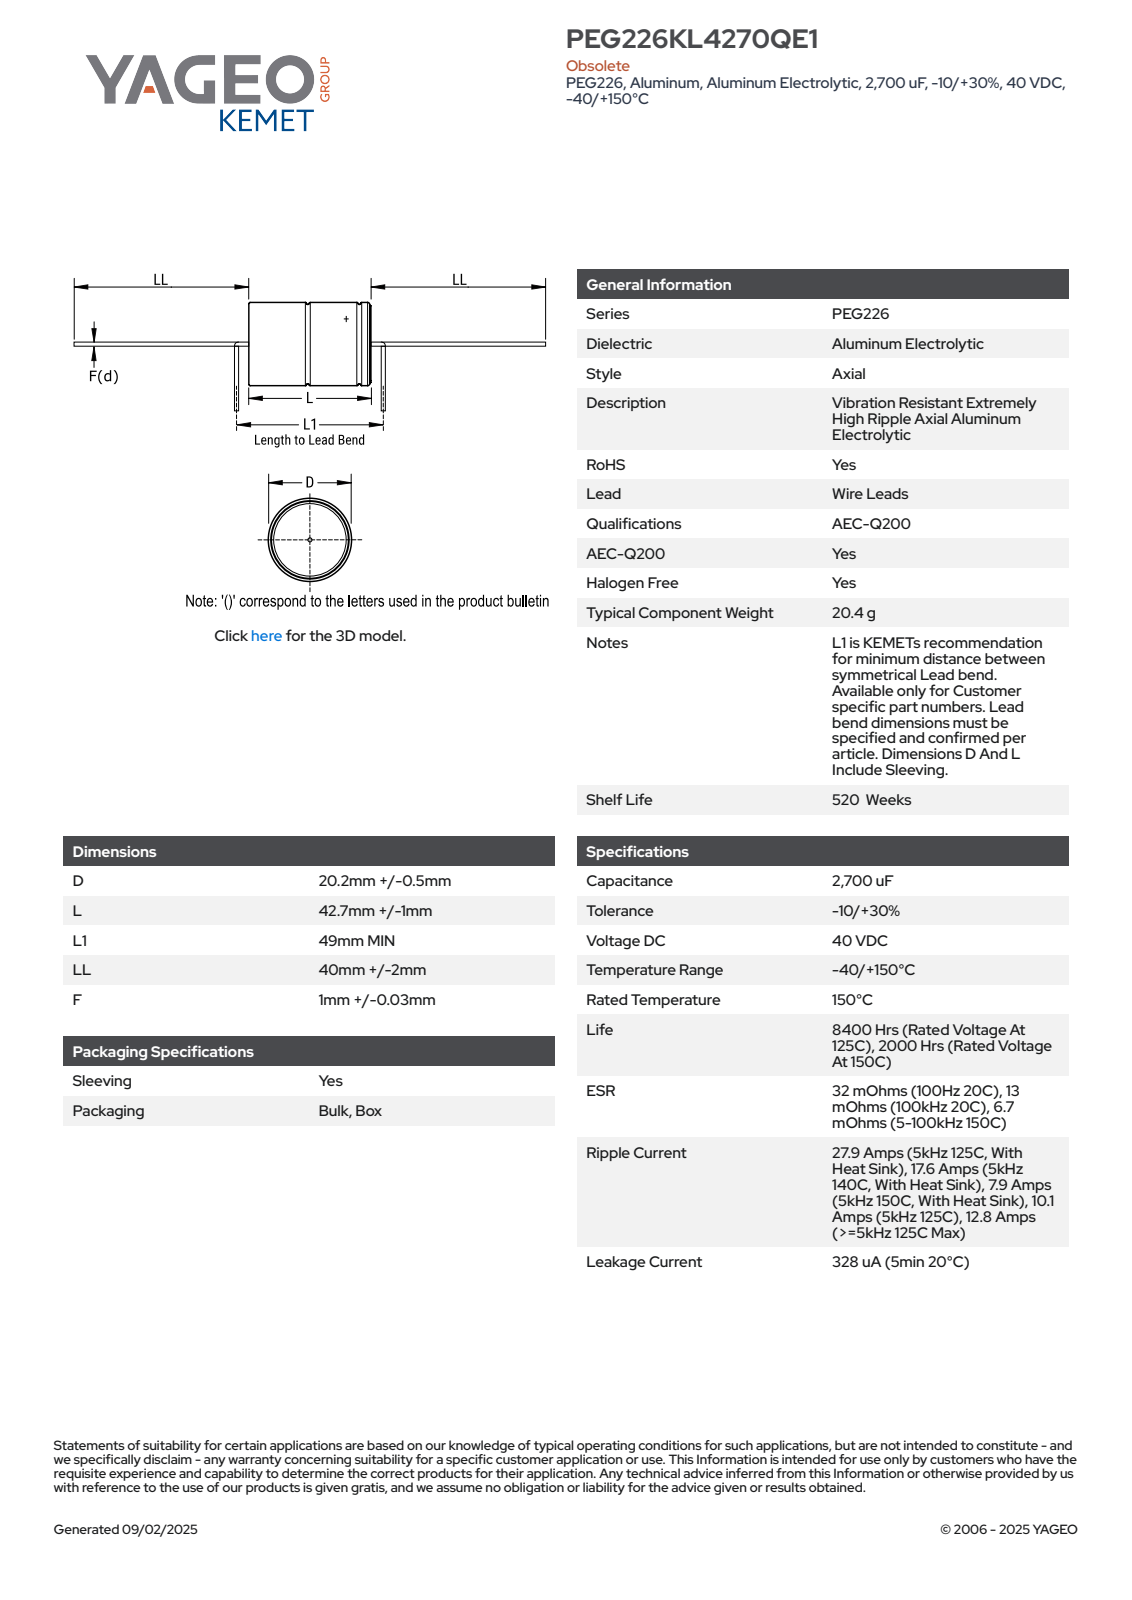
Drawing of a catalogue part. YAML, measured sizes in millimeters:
part_name: "CAA_PEG220_20X43_D20.7L43.7LL42F1.03"
step_written_by: "SolidWorks 2014 (AUTOMOTIVE_DESIGN)"
units: millimeters
bodies: {solids: 1, faces: 99, planar: 27, cylindrical: 29, other: 43}
overall_size: [127.7, 20.7, 20.7]
volume: 14463
surface_area: 3856
round_holes:
  - {diameter: 19.7, count: 1}
round_bosses_or_shafts:
  - {diameter: 20.7, count: 1}
  - {diameter: 20.2, count: 1}
  - {diameter: 1.03, count: 1}
partial_cylinders:
  - {radius: 10.34, count: 1}
face_to_face_distances: [42.7, 43.7, 1, 42, 85.7, 84.7, 127.7, 43]
